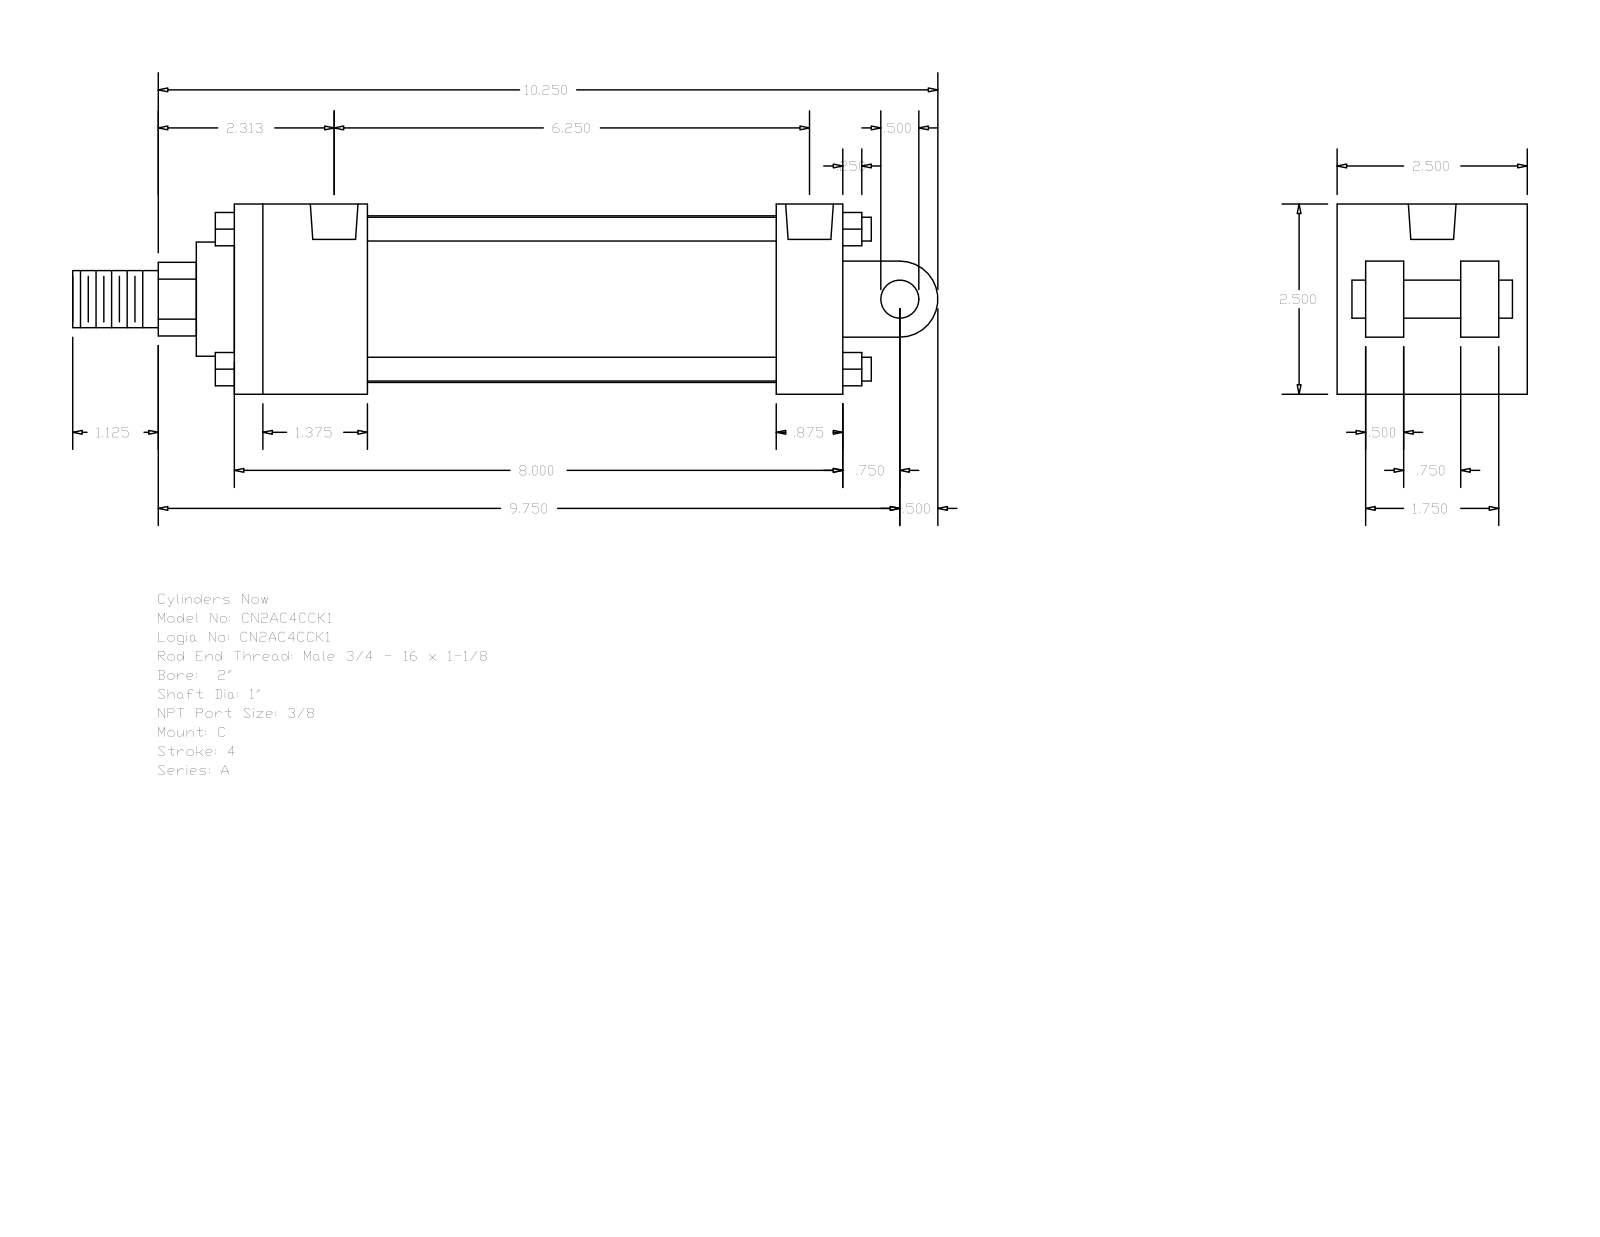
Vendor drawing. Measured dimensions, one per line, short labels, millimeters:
name: A_C__0200_1
written by: GSSL Pune (CONFIG_CONTROL_DESIGN)
unit: mm
bodies: 0 solids, 135 faces (102 planar, 33 cylindrical, 0 other)
size: 288.93 × 63.5 × 63.5
holes: 4× ⌀5.56, 2× ⌀15.93
bosses: 4× ⌀7.94, 1× ⌀55.63, 1× ⌀38.1, 1× ⌀25.4, 1× ⌀19.05, 1× ⌀12.7
rounds: 1× R12.29, 1× R12.7
face distances: 63.5, 22.22, 203.2, 44.45, 12.7, 9.52, 158.75, 180.98, 136.53, 41.28
hole spacings: 153.18, 1.59, 3.98, 154.77, 157.16, 158.75
